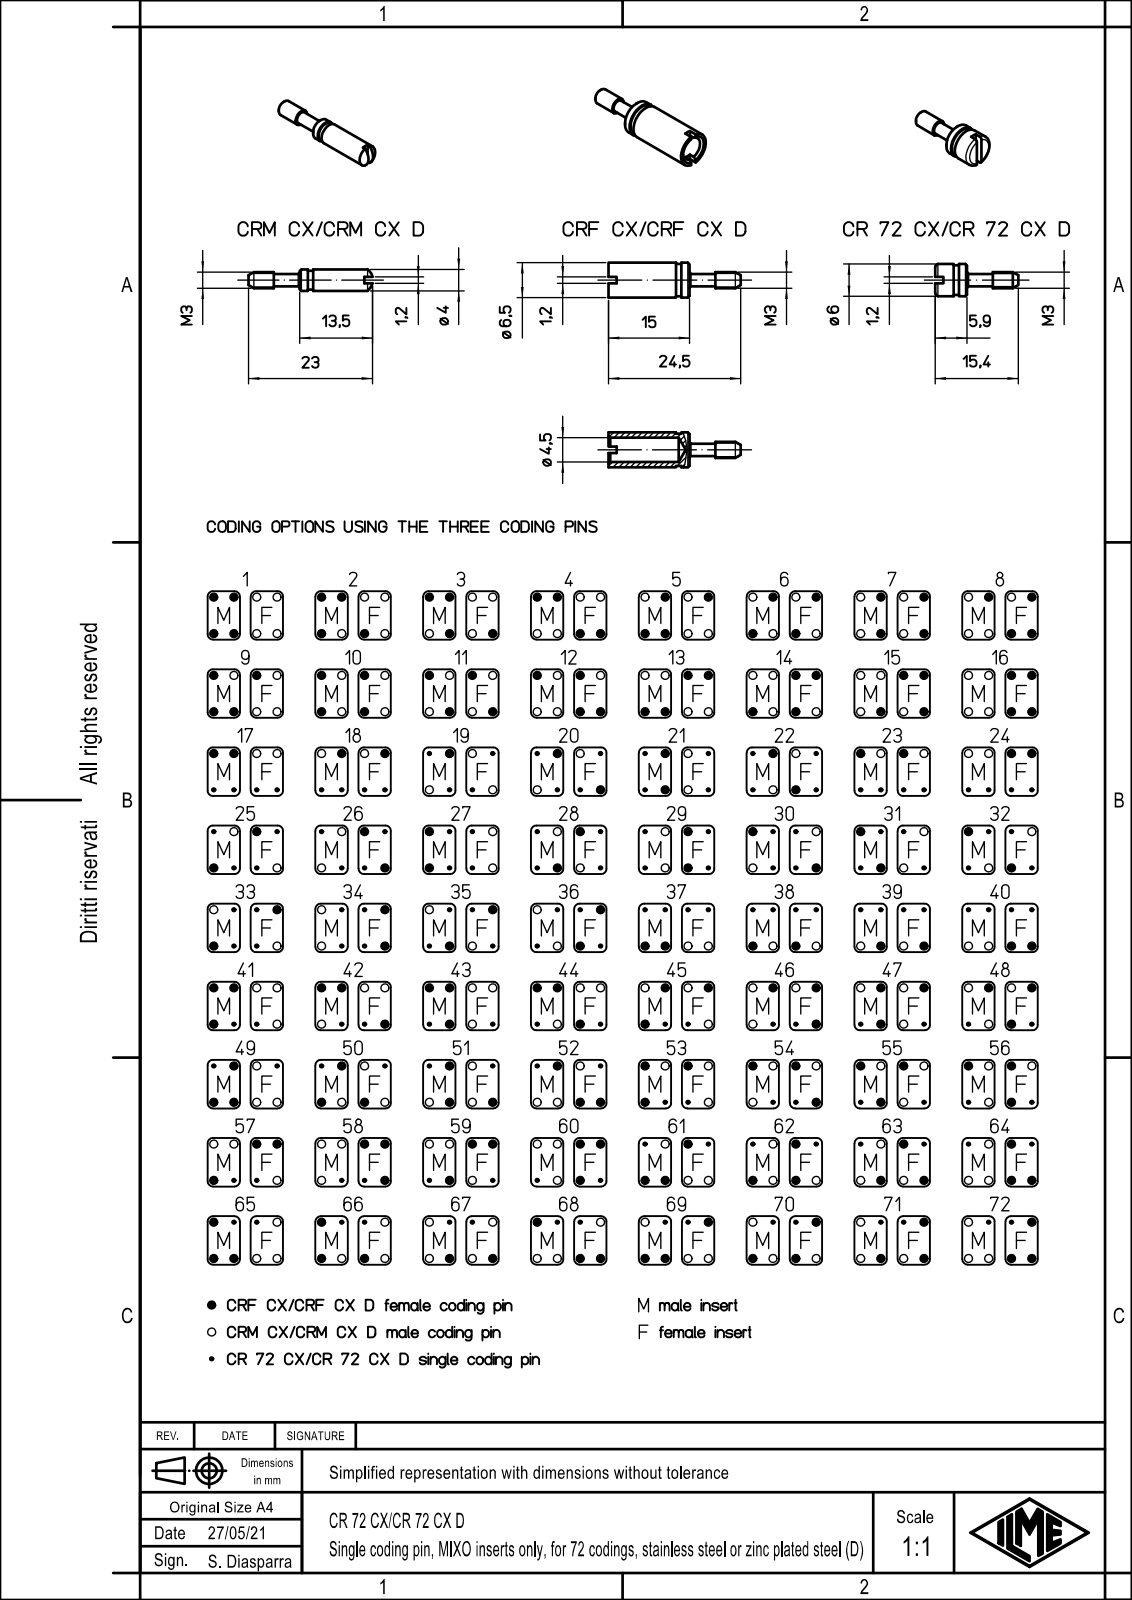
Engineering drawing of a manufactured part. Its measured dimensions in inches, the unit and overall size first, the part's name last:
Units: inches
Overall size (bounding box): 0.606 × 0.236 × 0.236
Round bosses / shafts (diameter × count): ⌀0.236 ×1, ⌀0.217 ×1, ⌀0.118 ×1, ⌀0.091 ×1
Main face-to-face distances: 0.232, 0.059, 0.173, 0.047, 0.098, 0.039, 0.114, 0.075, 0.134, 0.197
Volume: 0.012 in³ · Surface area: 0.403 in²
Bodies: 1 solid, 28 faces (10 planar, 10 cylindrical, 8 other)
Part name (STEP PRODUCT): CR_72_CX
STEP written by: Creo Elements/Direct Modeling 17.0D 15-Jul-2011 (C) Parametric Technology GmbH (AUTOMOTIVE_DESIGN)
